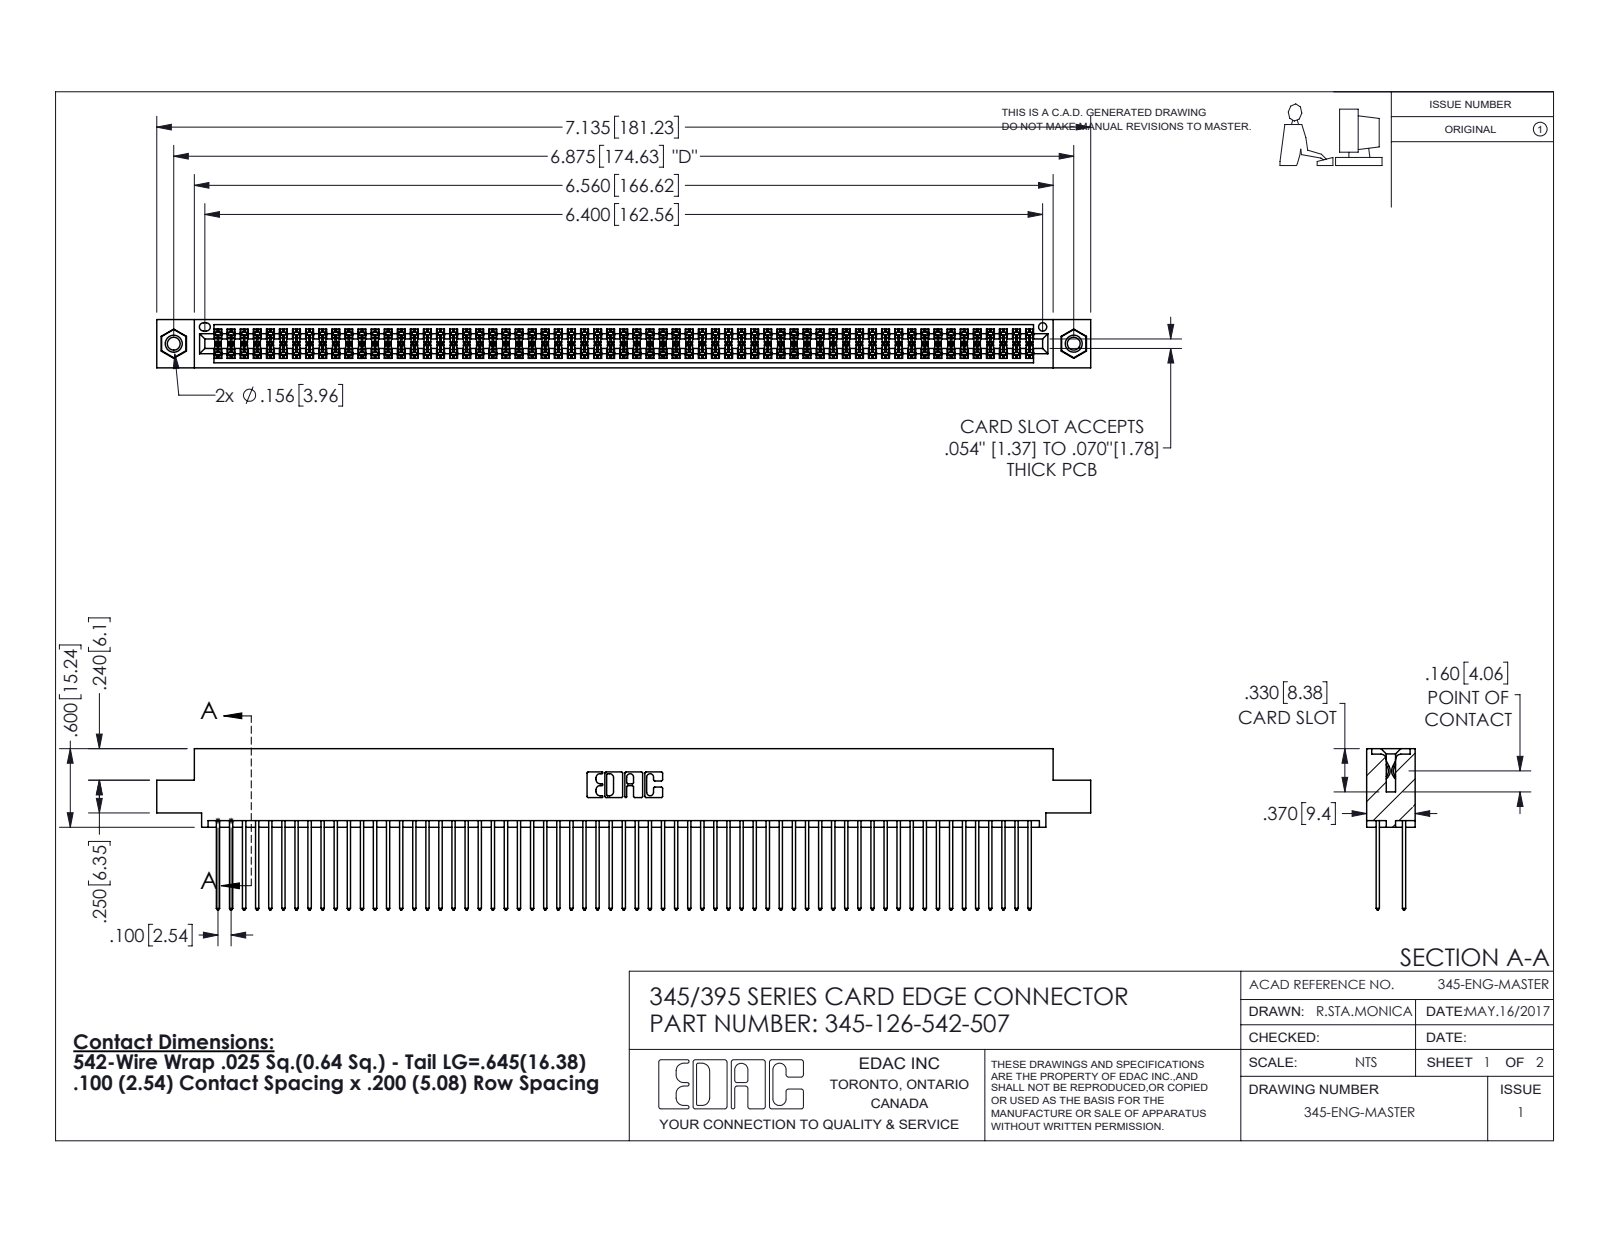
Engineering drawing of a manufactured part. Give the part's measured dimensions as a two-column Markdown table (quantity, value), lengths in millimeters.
| quantity | value |
| --- | --- |
| part name | 345 Part_0.110 Offset - 0.156 Dia-TI; 345-292-001_345-293-142; 345-126-542-507; 345-250-001_345-250-005-103 |
| STEP written by | SolidWorks 2016 (CONFIG_CONTROL_DESIGN) |
| units | millimeters |
| bodies | 129 solids, 6490 faces (4274 planar, 2200 cylindrical, 16 other) |
| overall size | 181.2 × 31.3 × 9.4 |
| volume | 18 300 mm³ |
| surface area | 30 320 mm² |
| round holes (diameter × count) | 2.5 × 2, 3.2 × 2, 4 × 2, 1.6 × 1 |
| round bosses / shafts (diameter × count) | 3.9 × 2 |
| partial cylindrical surfaces (radius × count) | 0.2 × 189, 0.3 × 126, 0.3 × 22, 0.2 × 6, 0.8 × 6, 0.7 × 3, 0.4 × 2, 0.5 × 2 |
| main face-to-face distances | 1.8, 7.6, 5.1, 2.5, 6.9, 0.6, 5.7, 9.4, 4.4, 3.8 |
| hole center spacings | 6.9, 168.6, 174.6 |
